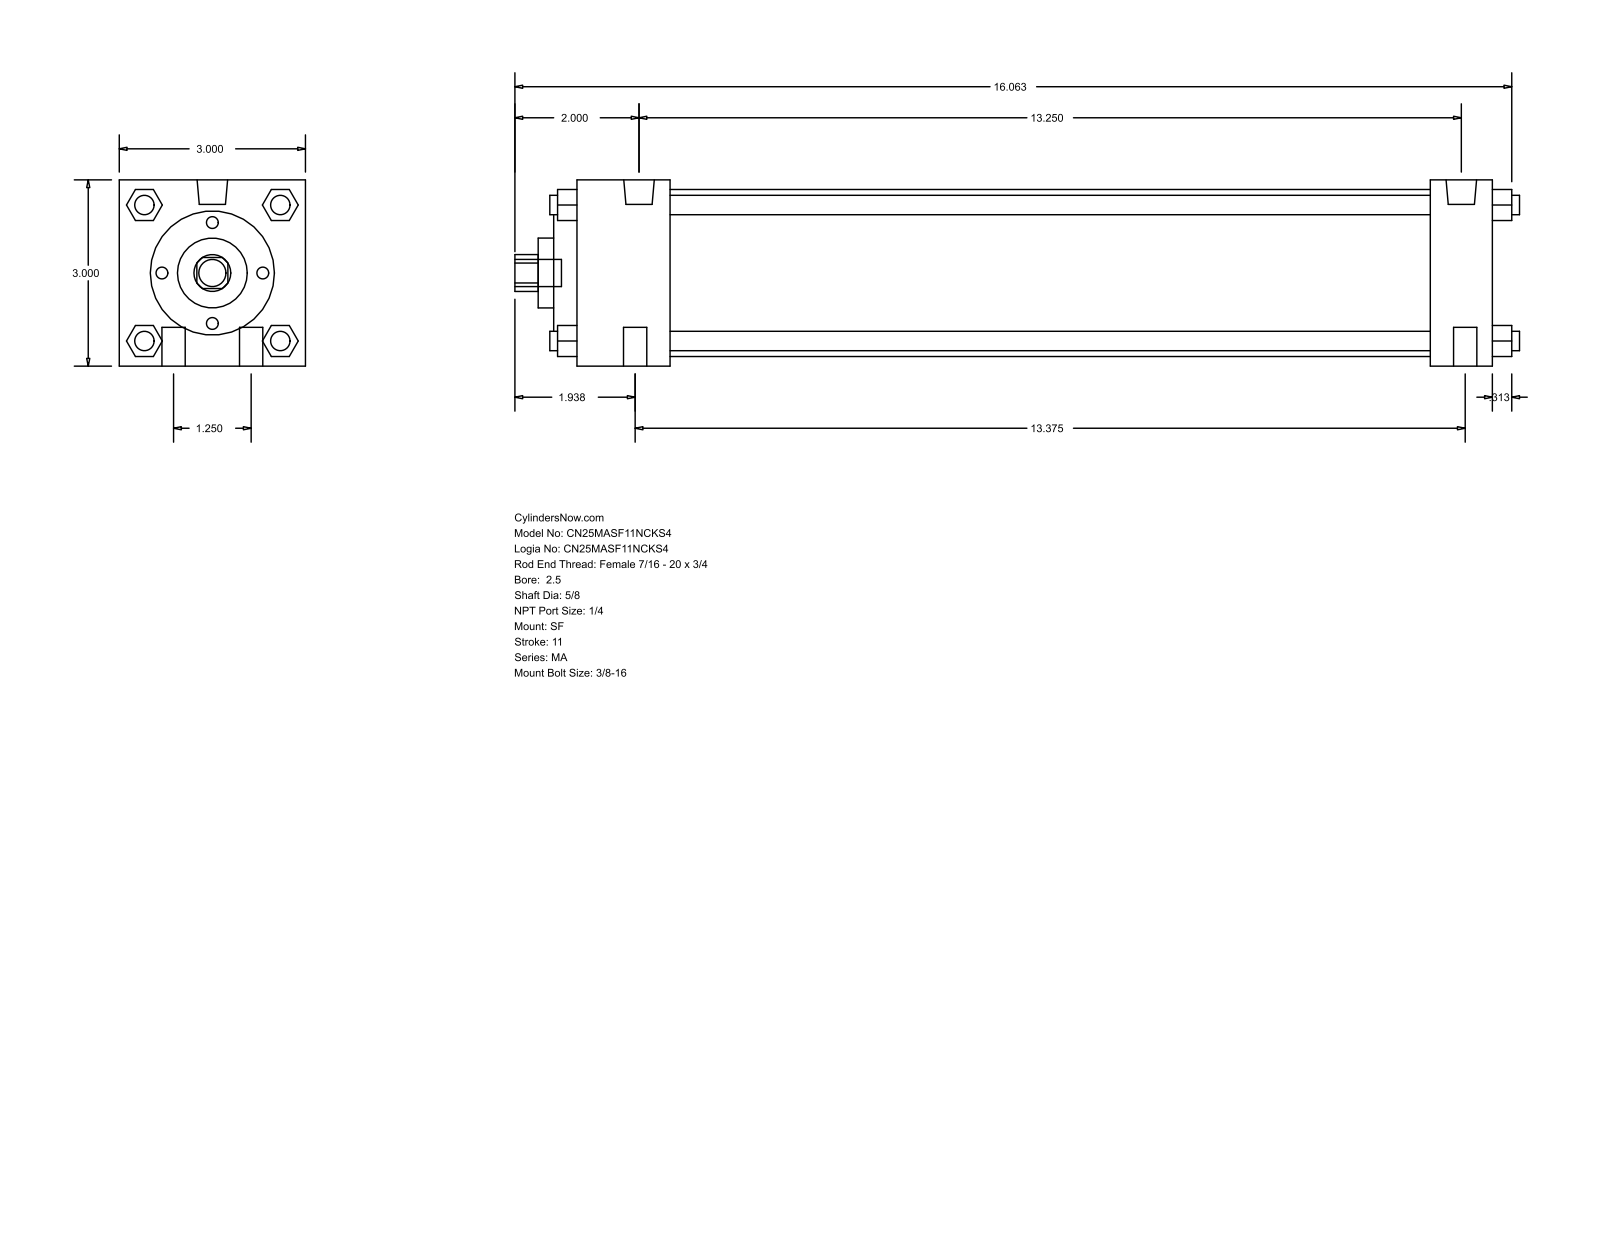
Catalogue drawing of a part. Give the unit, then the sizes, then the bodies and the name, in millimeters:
Units: millimetres
Overall size (bounding box): 411.16 × 76.2 × 76.2
Round holes (diameter × count): ⌀15.88 ×1, ⌀28.57 ×1, ⌀50.8 ×1, ⌀68.33 ×1
Round bosses / shafts (diameter × count): ⌀7.94 ×6, ⌀9.53 ×4, ⌀12.49 ×2, ⌀11.11 ×1
Partial cylindrical surfaces — rounded edges, fillets, slot ends (radius × count): R7.54 ×1
Main face-to-face distances: 76.2, 374.65, 25.4, 349.25, 38.1, 311.15, 336.55, 12.7, 9.52, 47.62
Bodies: 0 solids, 126 faces (95 planar, 31 cylindrical, 0 other)
Part name (STEP PRODUCT): MA_SF__0250_0.625
STEP written by: GSSL Pune (CONFIG_CONTROL_DESIGN)
